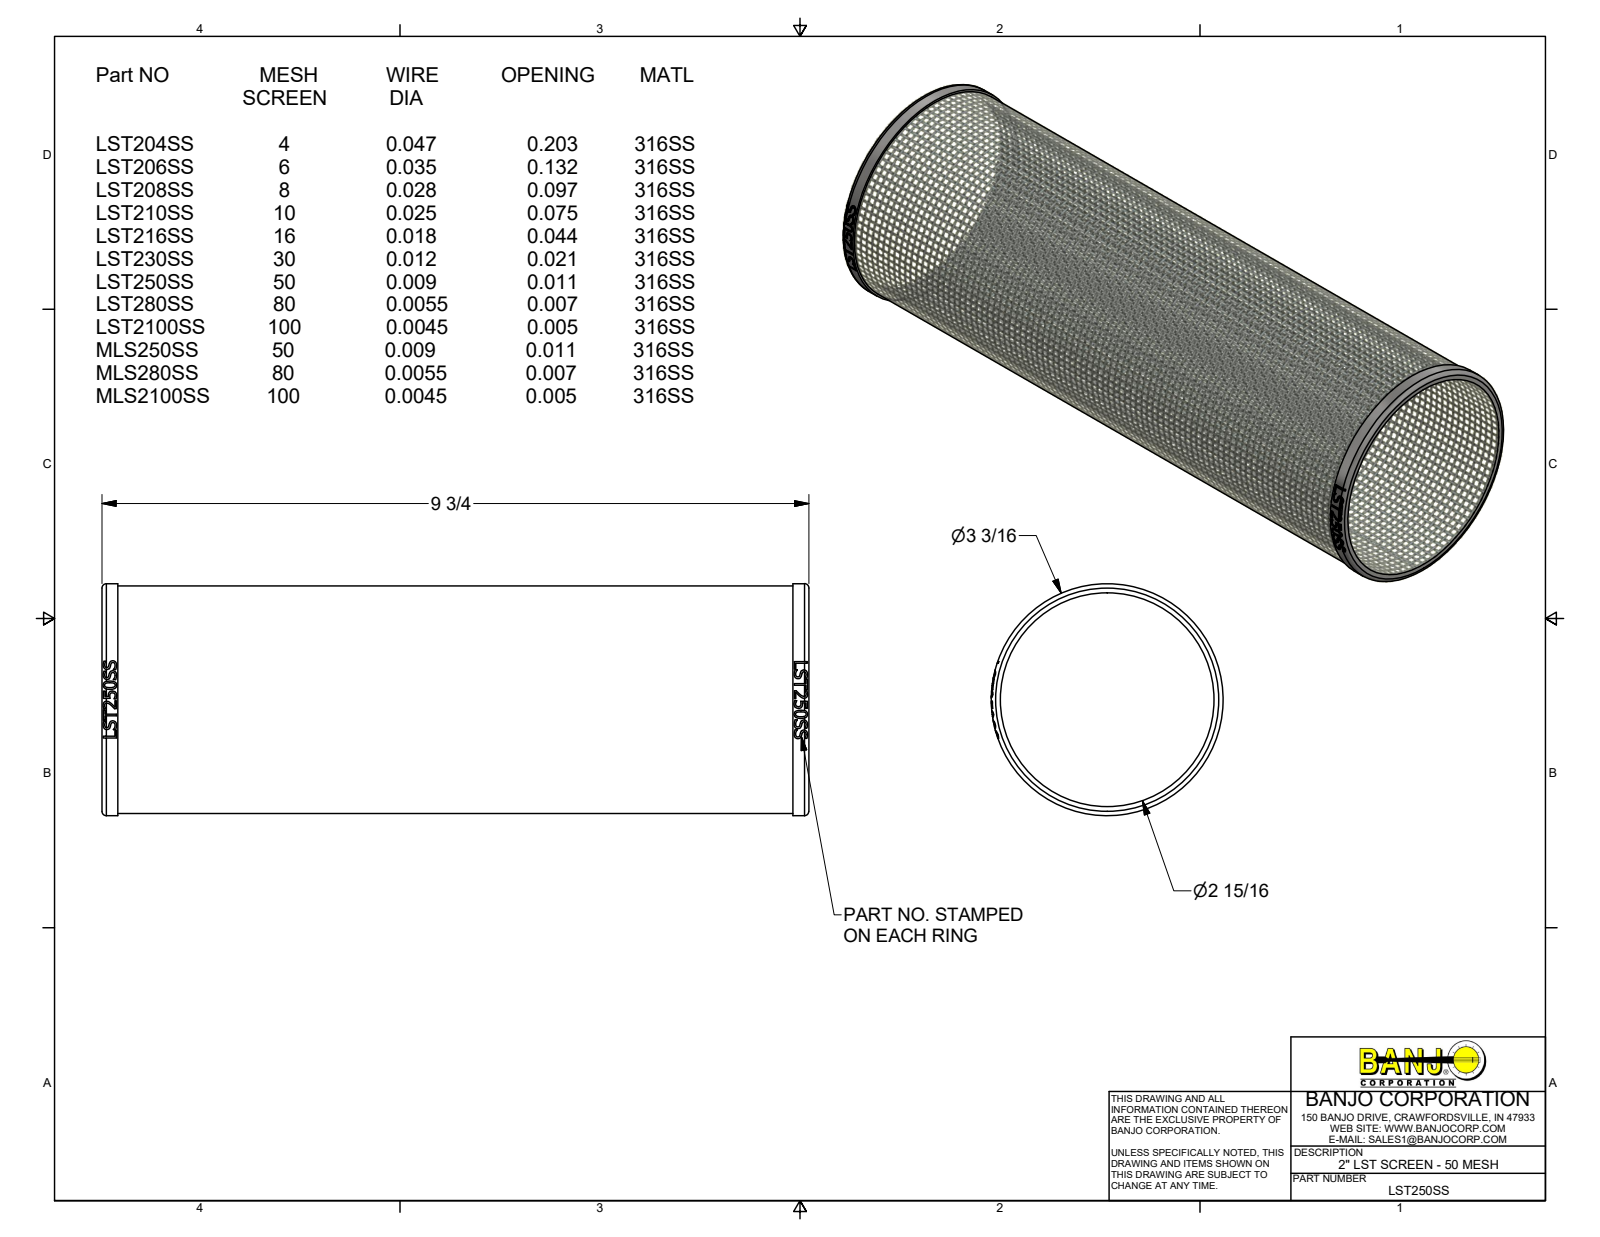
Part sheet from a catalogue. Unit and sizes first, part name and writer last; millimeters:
Units: millimetres
Overall size (bounding box): 246.89 × 80.97 × 80.97
Round holes (diameter × count): ⌀74.61 ×1
Round bosses / shafts (diameter × count): ⌀80.98 ×1, ⌀79.45 ×1
Partial cylindrical surfaces — rounded edges, fillets, slot ends (radius × count): R39.98 ×1
Main face-to-face distances: 246.89, 241.33, 5.56, 235.77, 4.53, 1.03, 0.49, 5.07, 4.03, 7.69
Volume: 146 393 mm³ · Surface area: 121 294 mm²
Bodies: 1 solid, 274 faces (82 planar, 22 cylindrical, 170 other)
Part name (STEP PRODUCT): LST250SS
STEP written by: Autodesk Inventor 2017 (AUTOMOTIVE_DESIGN)
